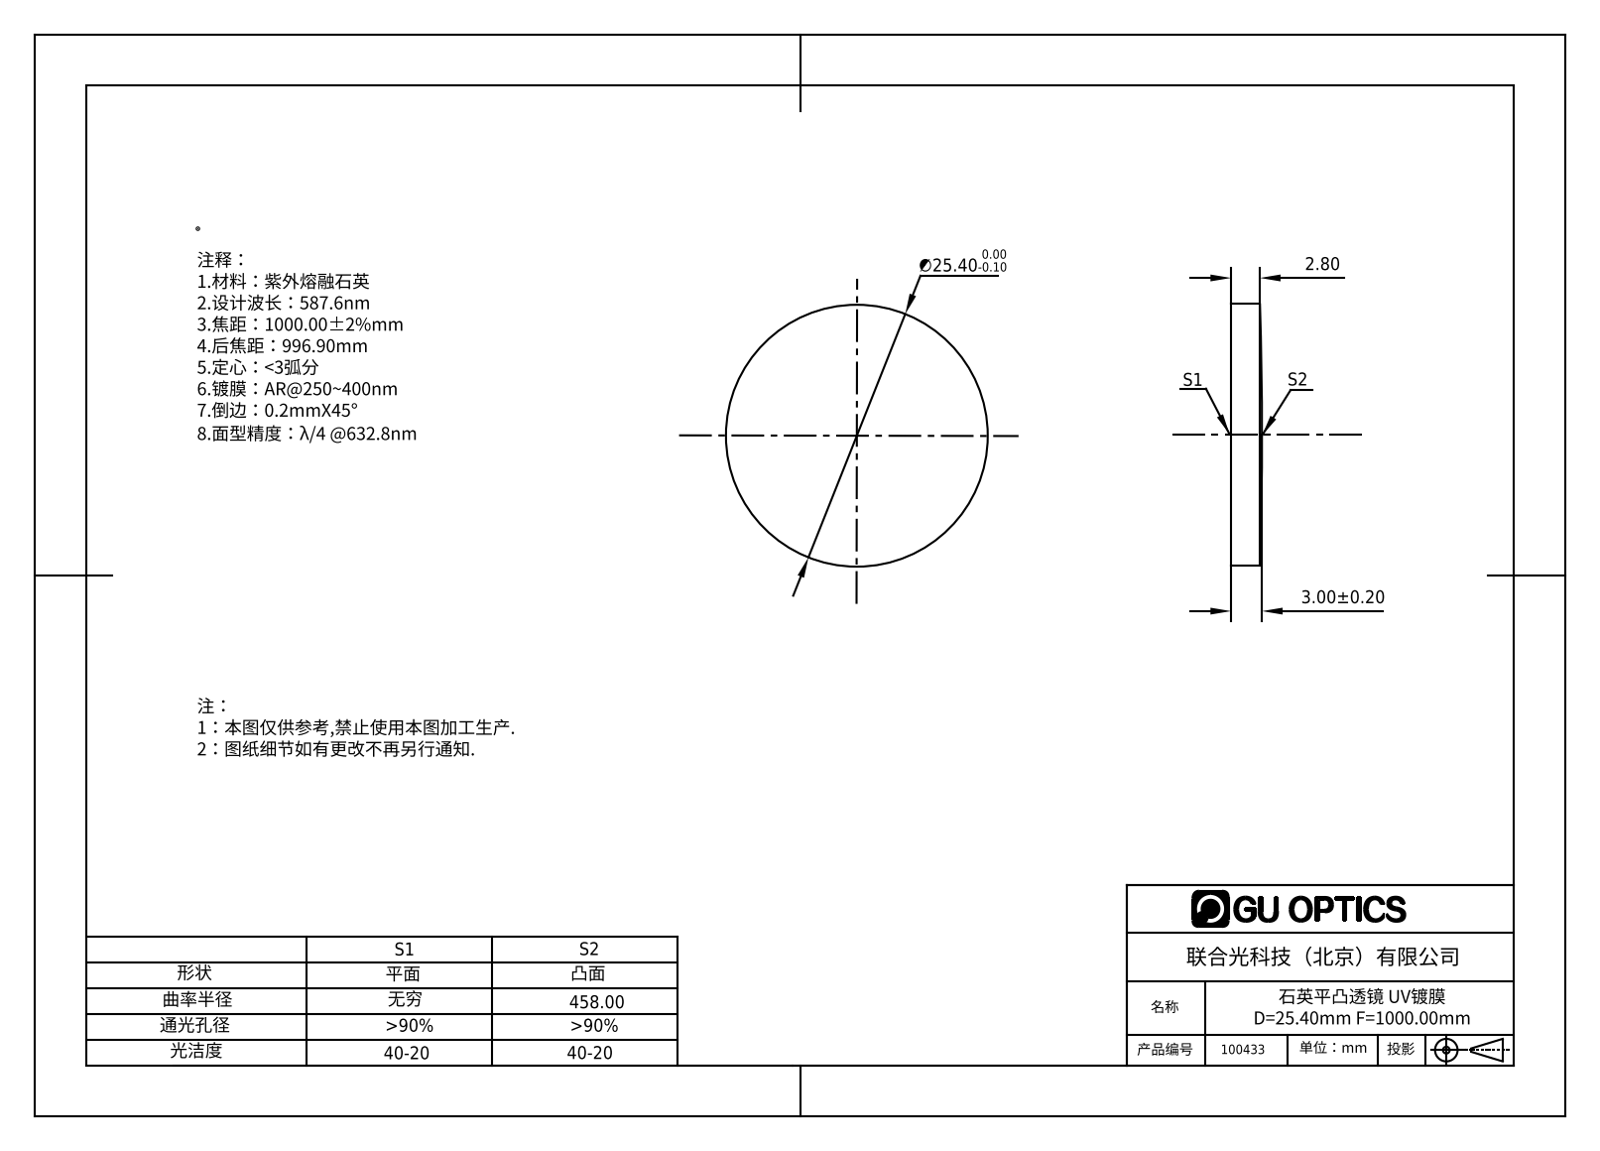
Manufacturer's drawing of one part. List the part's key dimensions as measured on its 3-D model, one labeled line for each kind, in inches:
Part name (STEP PRODUCT): 100383
STEP written by: SolidWorks 2016 (AUTOMOTIVE_DESIGN)
Units: inches
Bodies: 1 solid, 5 faces (1 planar, 2 cylindrical, 2 other)
Overall size (bounding box): 1 × 1 × 0.118
Volume: 0.09 in³ · Surface area: 1.917 in²
Round bosses / shafts (diameter × count): ⌀1 ×1
